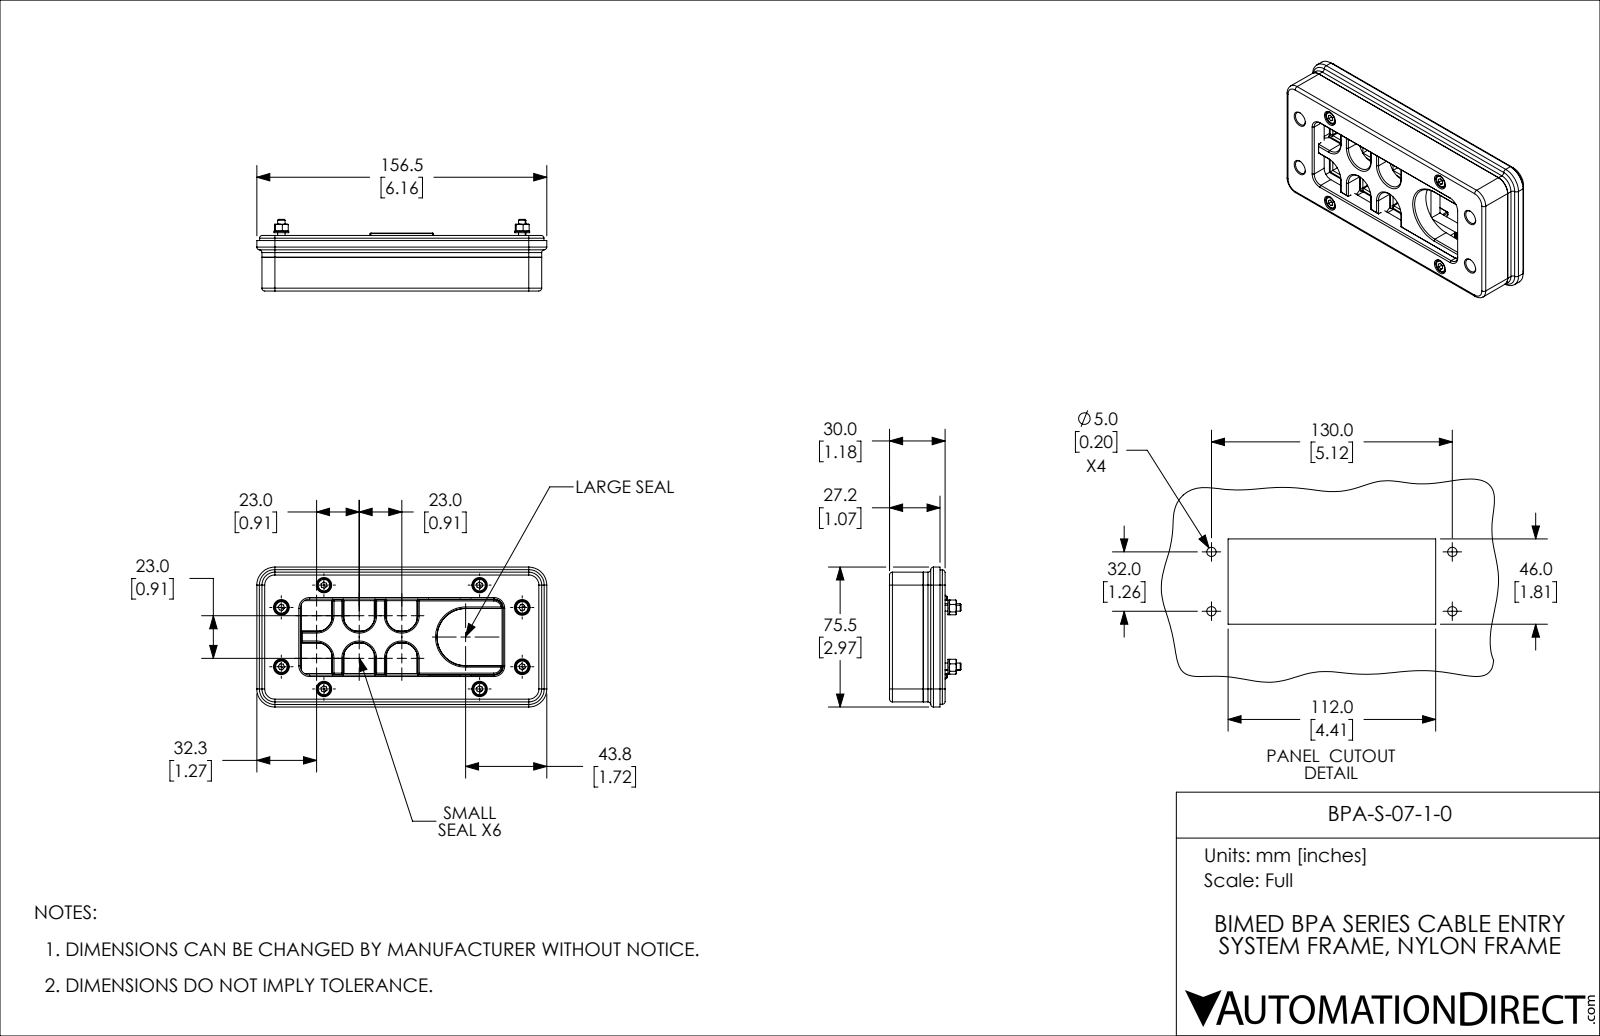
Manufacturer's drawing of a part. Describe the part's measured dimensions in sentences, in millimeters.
The part is named "BPA-S-07-1-0". Its 3-D file was written by "SolidWorks 2021 (CONFIG_CONTROL_DESIGN)". It is 29 solids with 1731 faces: 832 planar, 532 cylindrical and 367 other. Overall it measures 156.5 by 75.5 by 38.6 millimeters. Its volume is 184 882 cubic millimeters and its surface area 96 273 square millimeters. Round holes: 8 of diameter 3.24, 8 of diameter 4.5, 4 of diameter 4.3, 4 of diameter 5, 4 of diameter 7.3, 4 of diameter 7.5, 4 of diameter 8. Round bosses or shafts: 8 of diameter 7, 8 of diameter 4, 4 of diameter 8.1, 4 of diameter 8, 4 of diameter 6.9. Partial cylindrical surfaces (rounded edges, fillets, slot ends): 56 of radius 0.5, 20 of radius 1.5, 15 of radius 1, 10 of radius 0.4, 8 of radius 0.75, 4 of radius 3.4, 4 of radius 3.5, 4 of radius 4. The main face-to-face distances are 2.25, 2.5, 67.75, 27.2, 3, 18.8, 8.4, 9.6, 67.5, 65.25. The hole center spacings are 25.94, 49.65, 107.67, 115.69, 32, 56, 84, 100.96.
